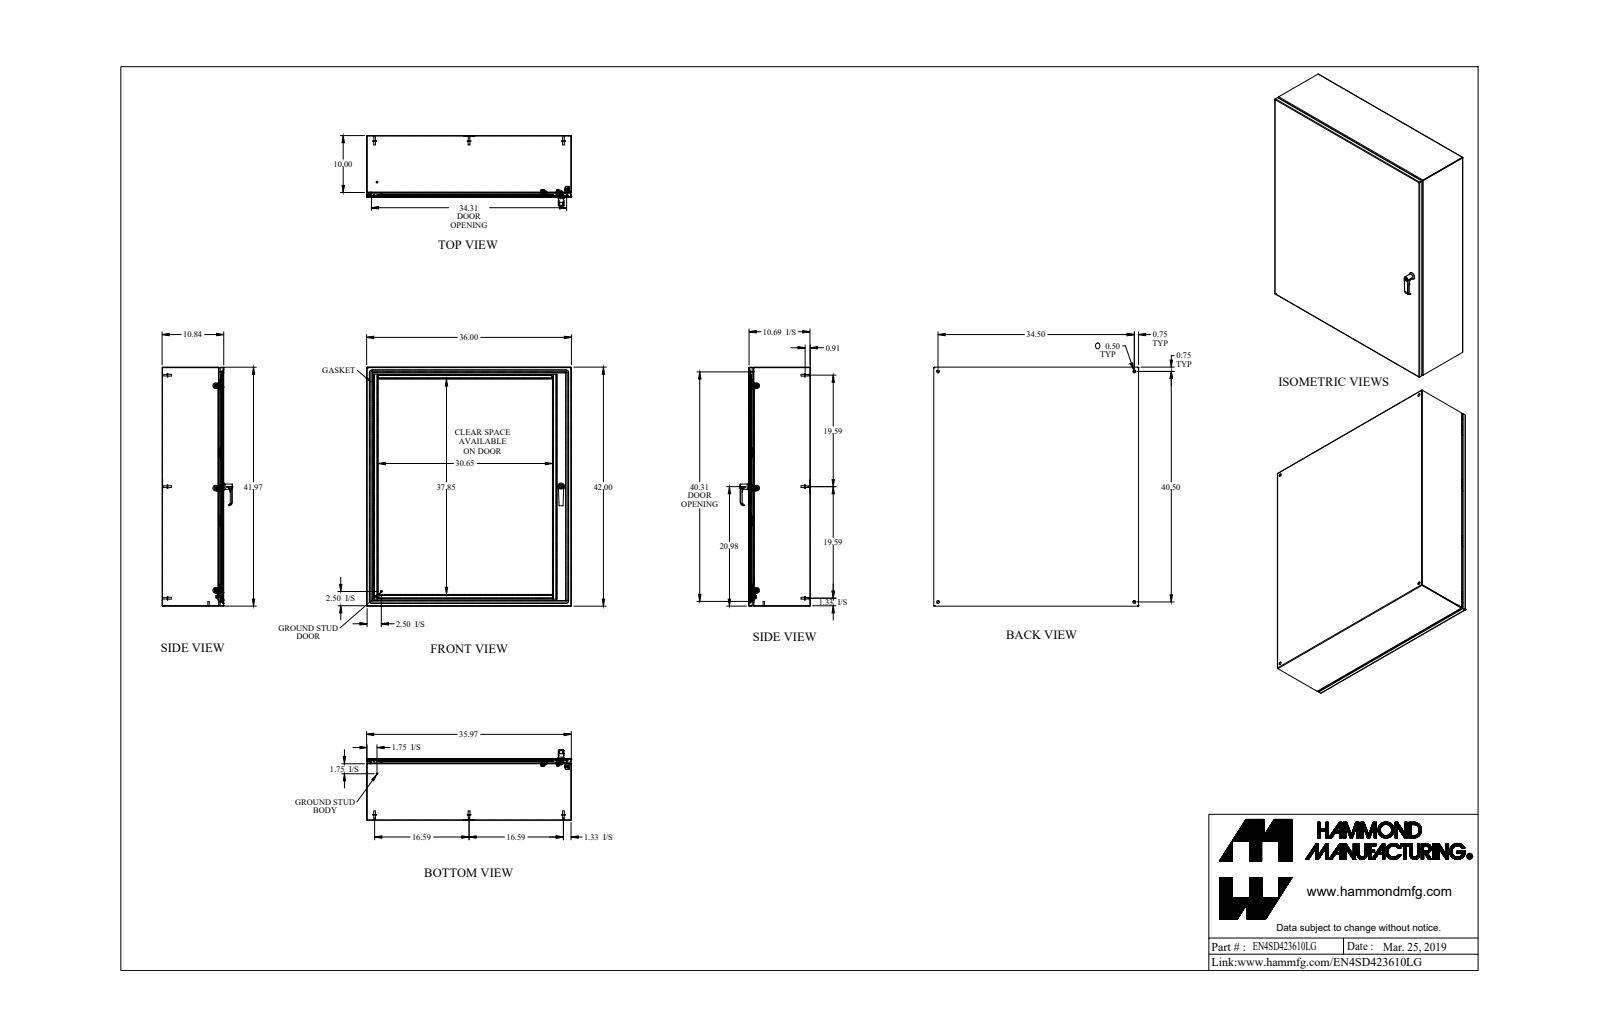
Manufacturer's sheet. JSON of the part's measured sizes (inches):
{"part_name": "EN4SD423610LG", "step_written_by": "SolidWorks 2019 (AUTOMOTIVE_DESIGN)", "units": "inches", "bodies": {"solids": 61, "faces": 1733, "planar": 757, "cylindrical": 638, "other": 338}, "overall_size": [42, 36, 12.367], "volume_in3": 386.7, "surface_area_in2": 10815, "round_holes": [[0.176, 6], [0.196, 4], [0.5, 4], [0.25, 3], [0.265, 3], [0.413, 3], [0.256, 2], [0.313, 2], [0.394, 2], [0.172, 1], [0.24, 1], [0.242, 1]], "round_bosses_or_shafts": [[0.313, 8], [0.27, 8], [0.25, 7], [0.625, 6], [0.375, 6], [0.156, 6], [1, 3], [0.625, 3]], "partial_cylinders_radius": [[0.043, 24], [0.081, 24], [0.036, 20], [0.108, 20], [0.03, 15], [0.062, 12], [0.094, 10], [0.016, 9]], "face_to_face_distances": [0.072, 10.765, 10.693, 10.837, 35.928, 41.928, 35.856, 36, 41.856, 42], "hole_center_spacings": [0.787, 2.507, 17.981, 17.988, 18, 33.504, 34.5, 35.969]}
